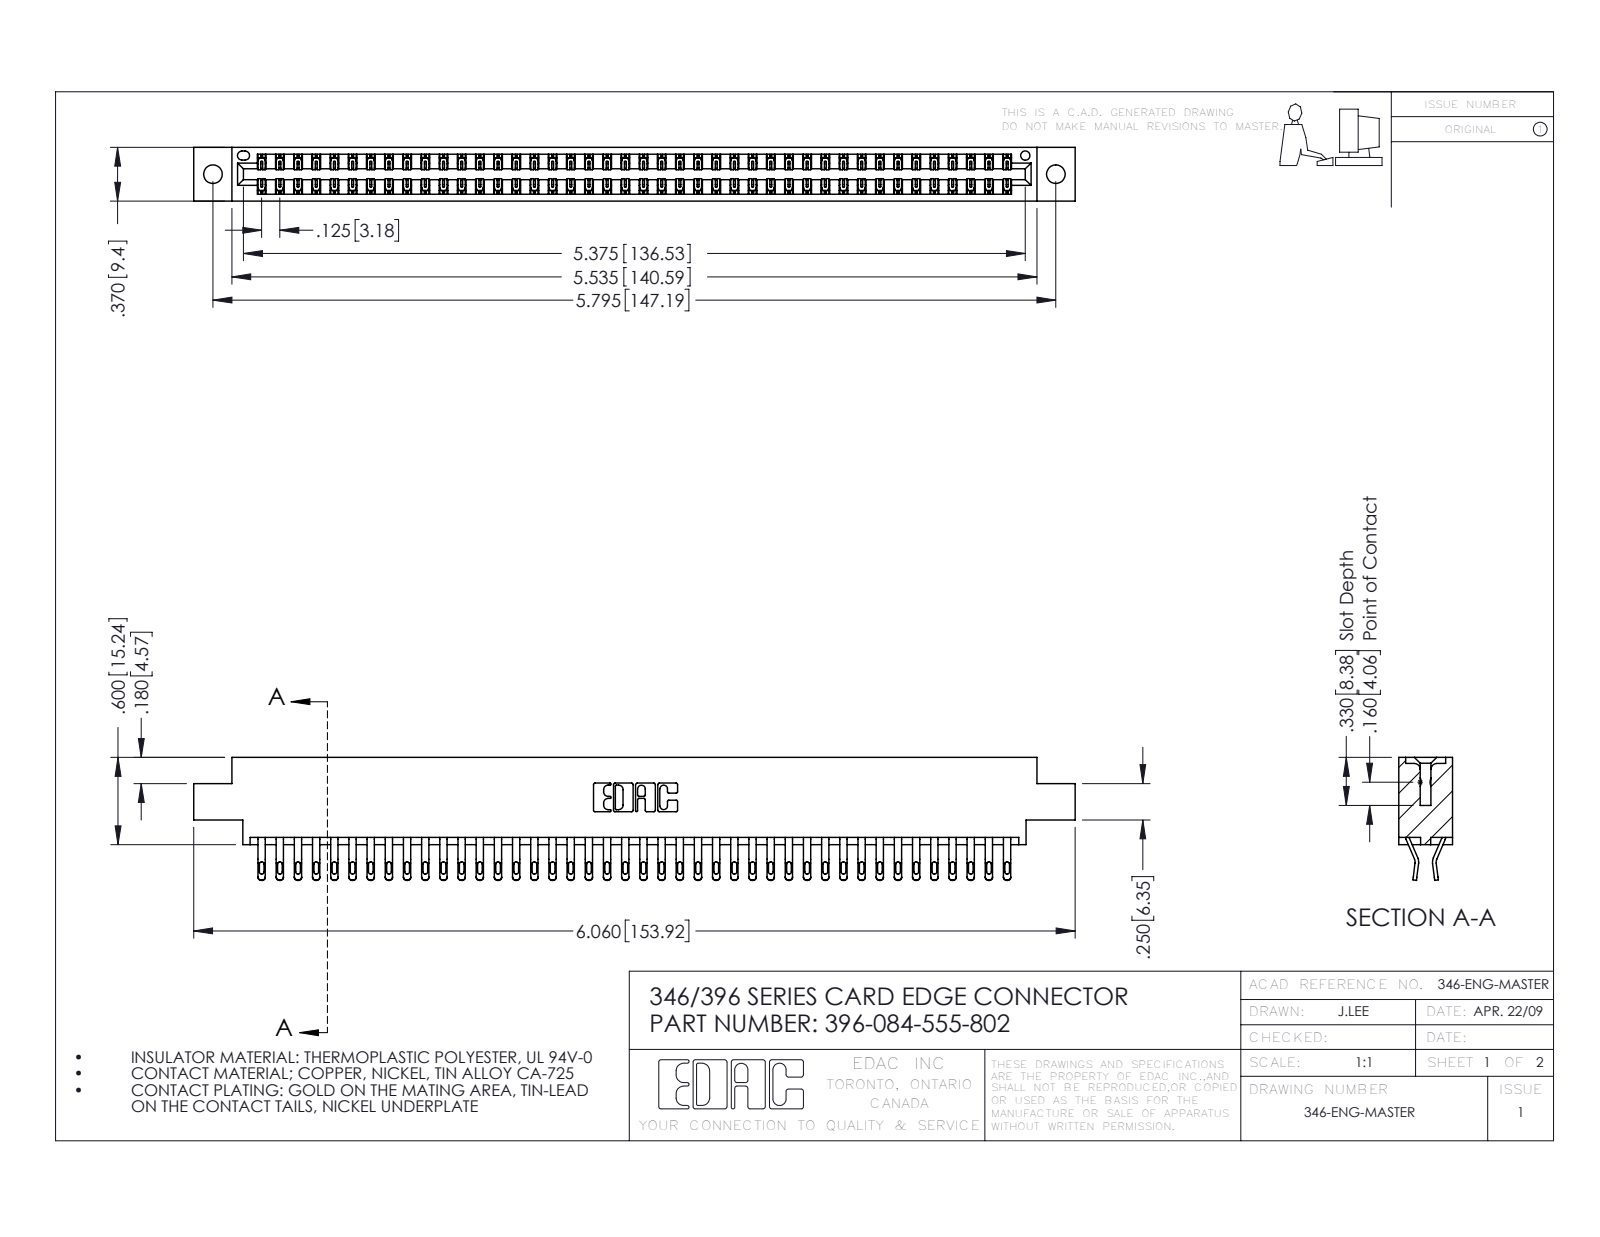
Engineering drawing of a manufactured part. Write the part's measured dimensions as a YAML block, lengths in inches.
part_name: "346 Part_0.170 Offset - 0.128 Dia; 345-292-001_555 Tail; 396-084-555-802"
step_written_by: "SolidWorks 2016 (CONFIG_CONTROL_DESIGN)"
units: inches
bodies: {solids: 85, faces: 4998, planar: 2852, cylindrical: 2146, other: 0}
overall_size: [6.06, 0.845, 0.37]
volume: 0.919
surface_area: 33.3
round_holes:
  - {diameter: 0.128, count: 2}
  - {diameter: 0.064, count: 1}
partial_cylinders:
  - {radius: 0.016, count: 168}
  - {radius: 0.02, count: 168}
  - {radius: 0.006, count: 126}
  - {radius: 0.01, count: 22}
  - {radius: 0.007, count: 6}
  - {radius: 0.031, count: 6}
  - {radius: 0.026, count: 3}
  - {radius: 0.01, count: 2}
face_to_face_distances: [0.048, 0.322, 0.37, 0.25, 0.025, 0.072, 0.298, 0.275, 0.148, 0.222]
hole_center_spacings: [0.246, 5.586, 5.795]
